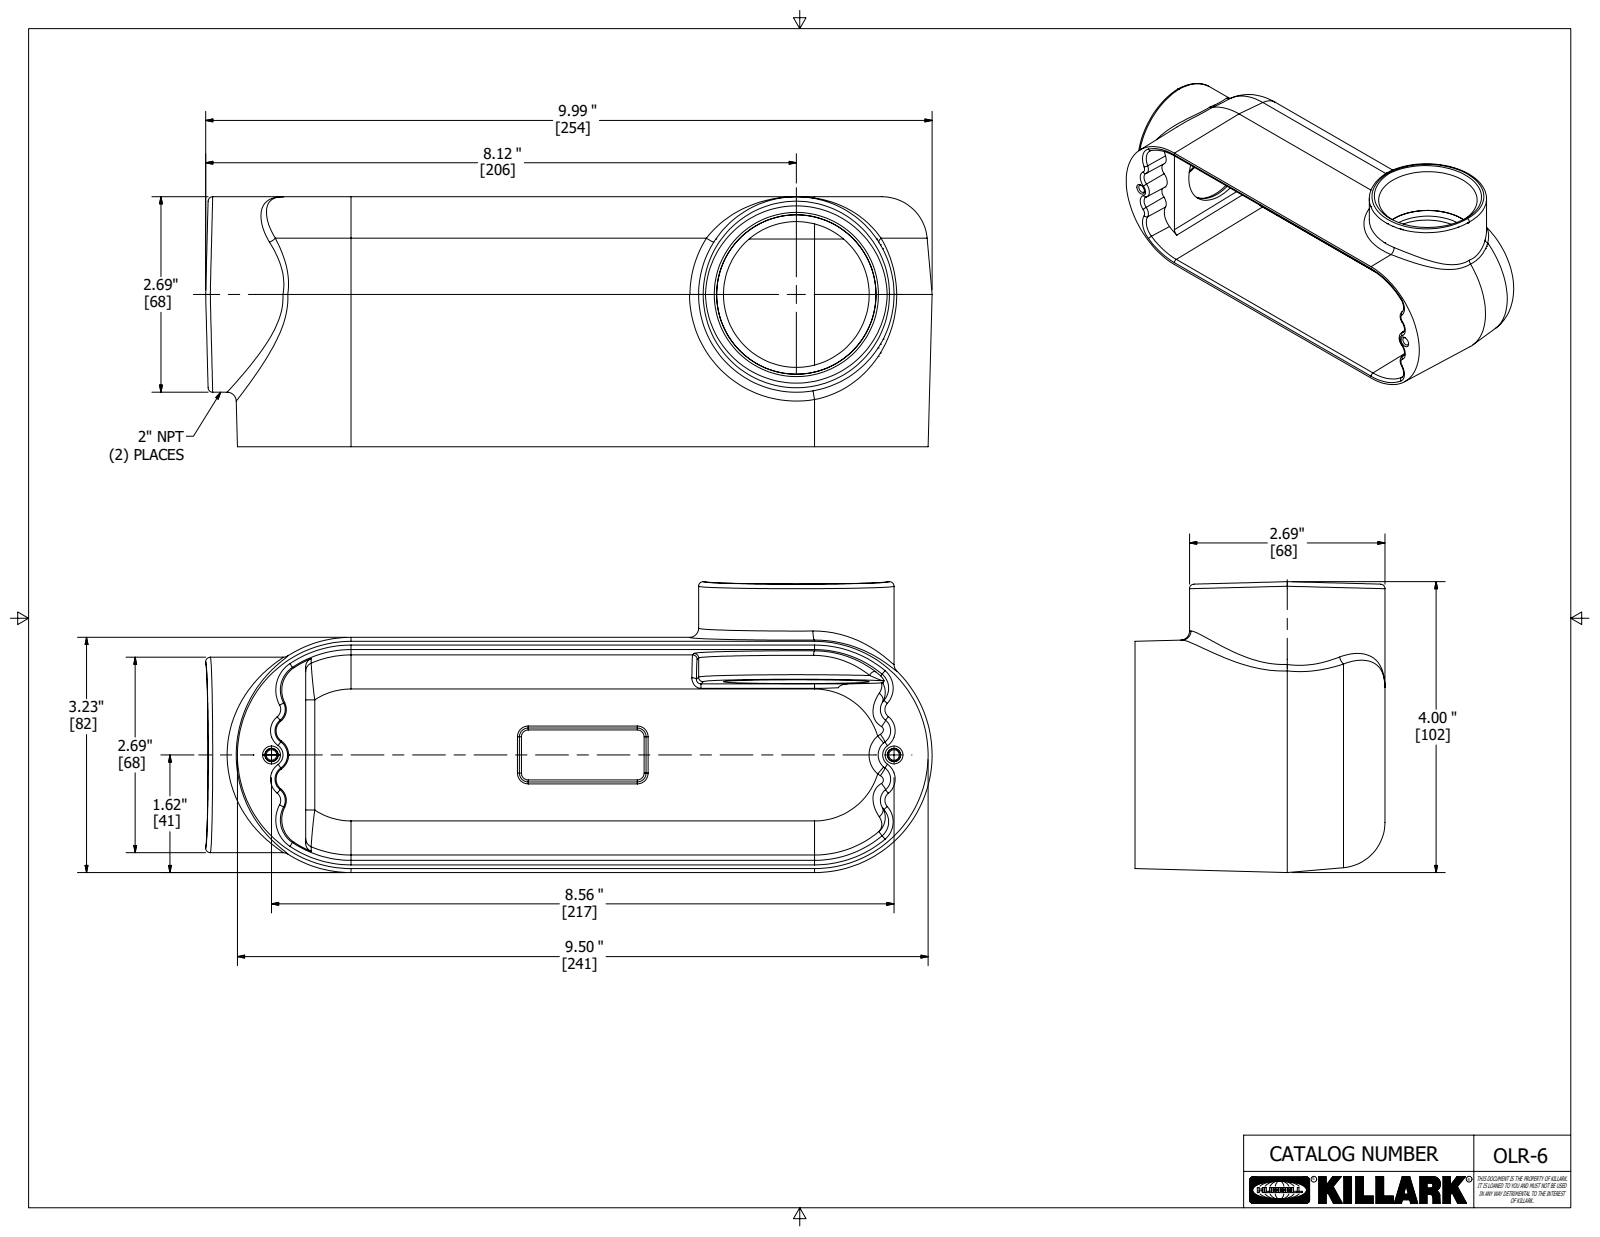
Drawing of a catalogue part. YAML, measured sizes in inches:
part_name: "18030-1"
step_written_by: "Autodesk Inventor 2018 (AUTOMOTIVE_DESIGN)"
units: inches
bodies: {solids: 1, faces: 173, planar: 27, cylindrical: 38, other: 108}
overall_size: [9.992, 4, 3.438]
volume: 20.96
surface_area: 209.7
round_holes:
  - {diameter: 2.004, count: 2}
round_bosses_or_shafts:
  - {diameter: 2.688, count: 2}
partial_cylinders:
  - {radius: 0.031, count: 16}
  - {radius: 0.062, count: 5}
  - {radius: 0.187, count: 4}
  - {radius: 0.469, count: 2}
  - {radius: 0.625, count: 2}
  - {radius: 0.125, count: 1}
  - {radius: 0.219, count: 1}
face_to_face_distances: [3.013, 0.125, 3.437, 3.312, 0.388, 2.625, 0.156, 0.031, 3.281, 0.031]
